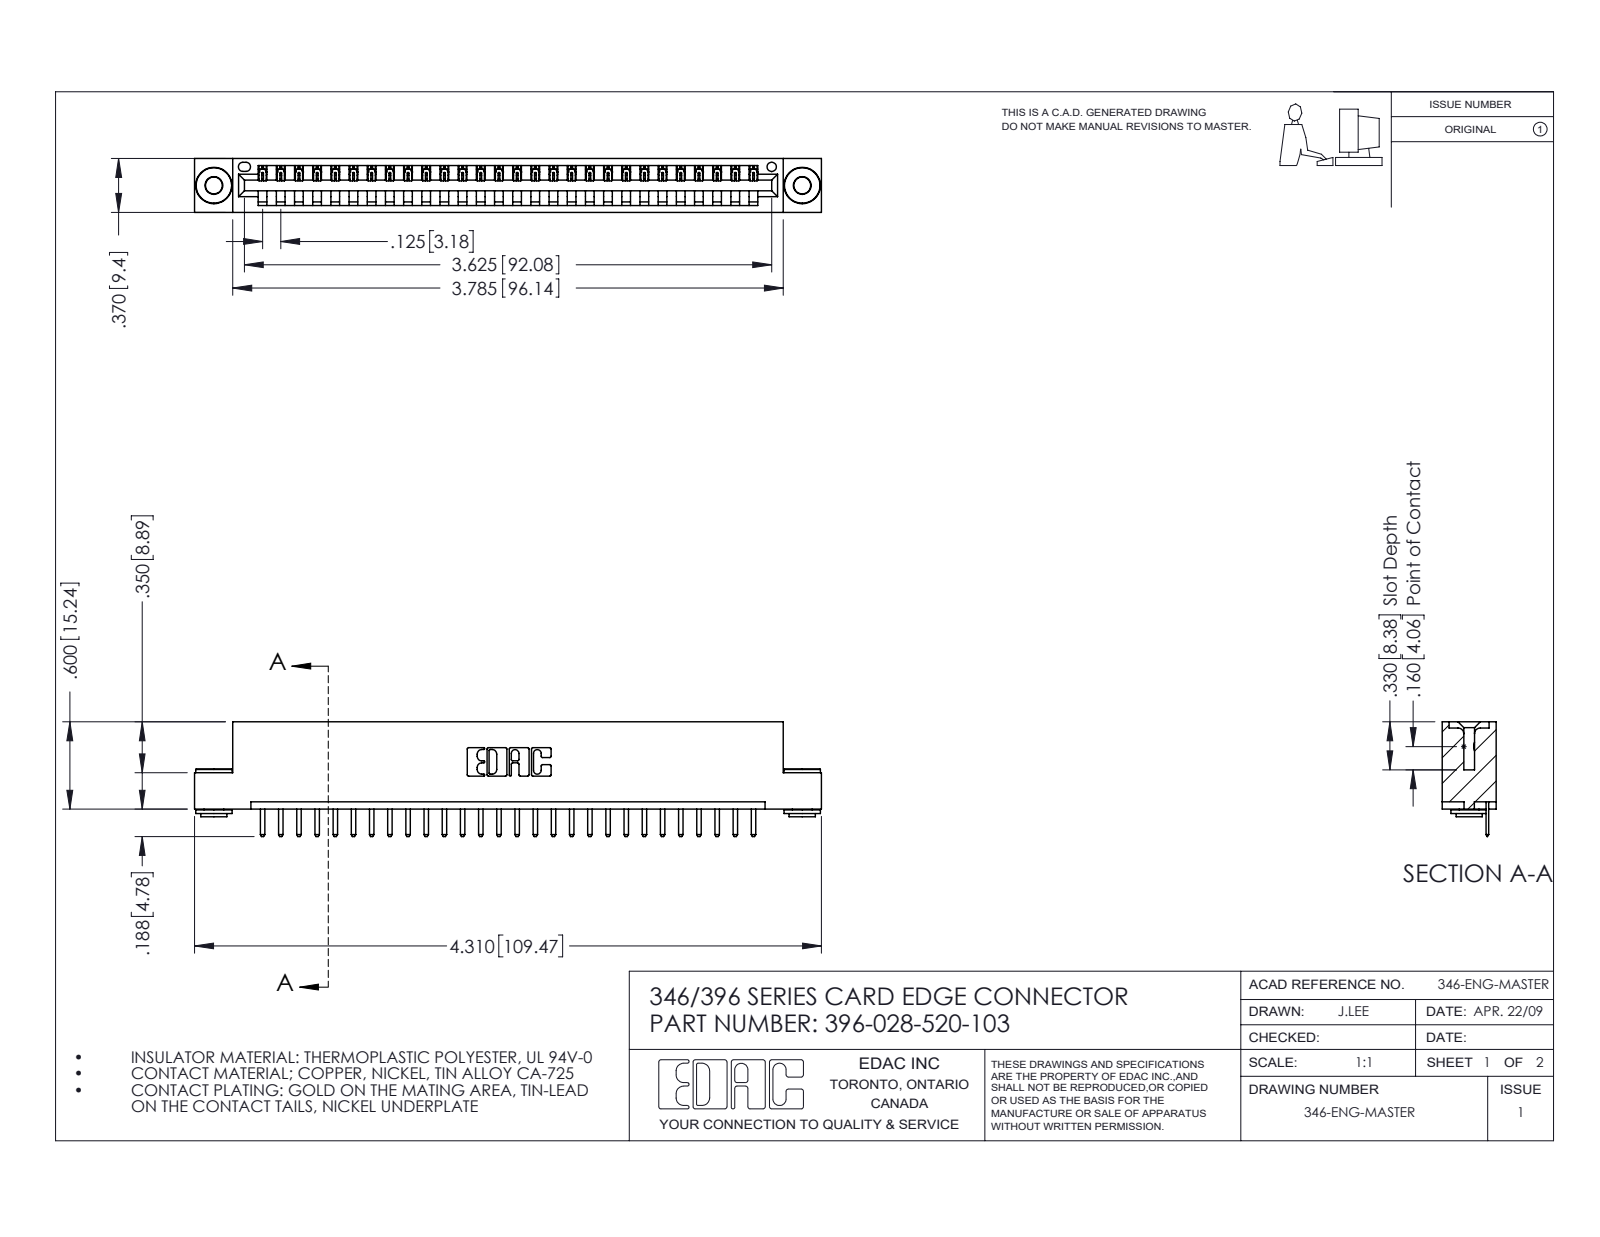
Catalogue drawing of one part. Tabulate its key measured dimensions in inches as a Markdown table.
| quantity | value |
| --- | --- |
| part name | 396-028-520-103; 346 Part_Flush Mounting Lugs - 0.156 Dia-TH; 345-292-001_345-293-120; 345-250-002_345-250-002-102 |
| STEP written by | SolidWorks 2016 (CONFIG_CONTROL_DESIGN) |
| units | inches |
| bodies | 31 solids, 1896 faces (1262 planar, 626 cylindrical, 8 other) |
| overall size | 4.31 × 0.788 × 0.37 |
| volume | 0.63 in³ |
| surface area | 19.68 in² |
| round holes (diameter × count) | 0.116 × 2, 0.156 × 2, 0.064 × 1 |
| round bosses / shafts (diameter × count) | 0.25 × 2, 0.18 × 2, 0.136 × 2 |
| partial cylindrical surfaces (radius × count) | 0.01 × 58, 0.006 × 56, 0.01 × 22, 0.007 × 6, 0.031 × 6, 0.026 × 3, 0.031 × 2, 0.04 × 2 |
| main face-to-face distances | 0.048, 0.322, 0.37, 0.25, 0.148, 0.222, 0.1, 0.174, 0.025, 0.072 |
| hole center spacings | 0.246, 3.837, 4.045 |
